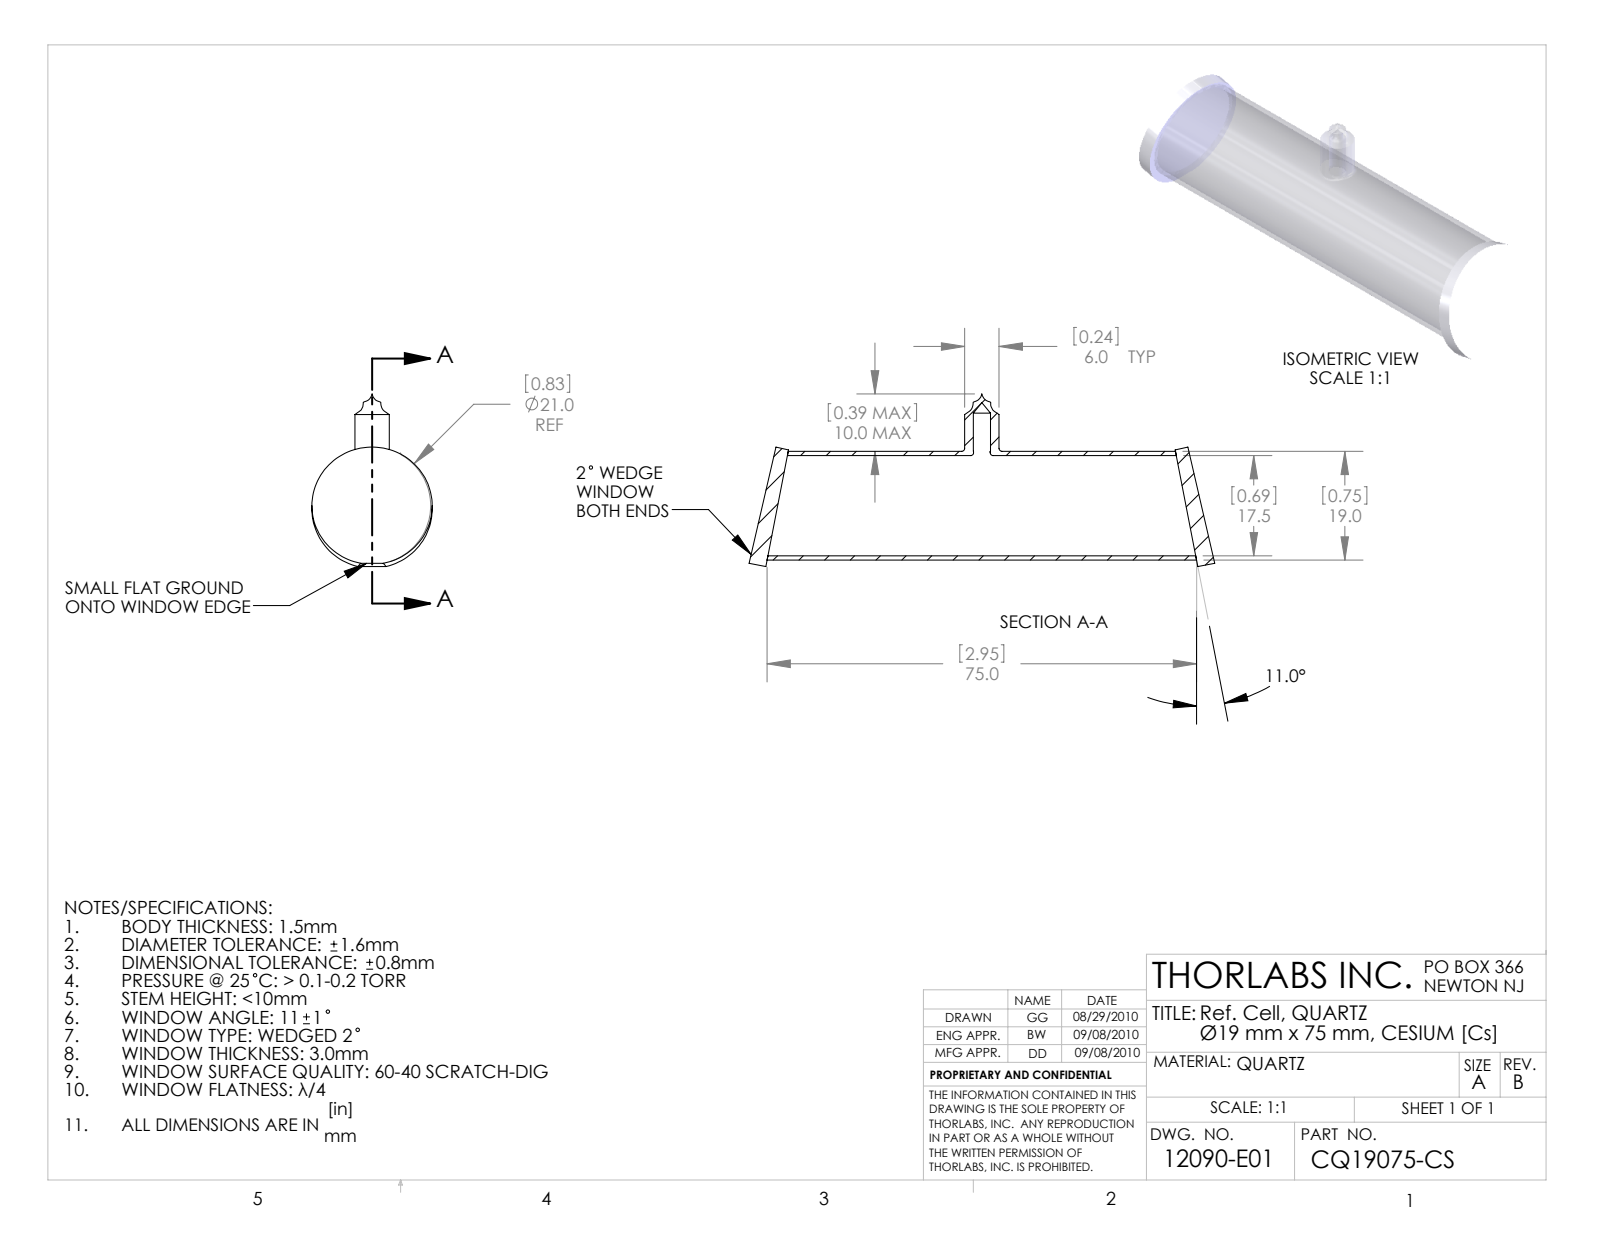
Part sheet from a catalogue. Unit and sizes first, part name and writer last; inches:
Units: inches
Overall size (bounding box): 3.201 × 1.186 × 0.827
Round holes (diameter × count): ⌀0.115 ×1, ⌀0.118 ×1, ⌀0.689 ×1
Round bosses / shafts (diameter × count): ⌀0.827 ×2, ⌀0.748 ×1, ⌀0.236 ×1
Volume: 0.308 in³ · Surface area: 15.82 in²
Bodies: 3 solids, 33 faces (8 planar, 17 cylindrical, 8 other)
Part name (STEP PRODUCT): 12090-E0W
STEP written by: SolidWorks 2009 (AUTOMOTIVE_DESIGN)
